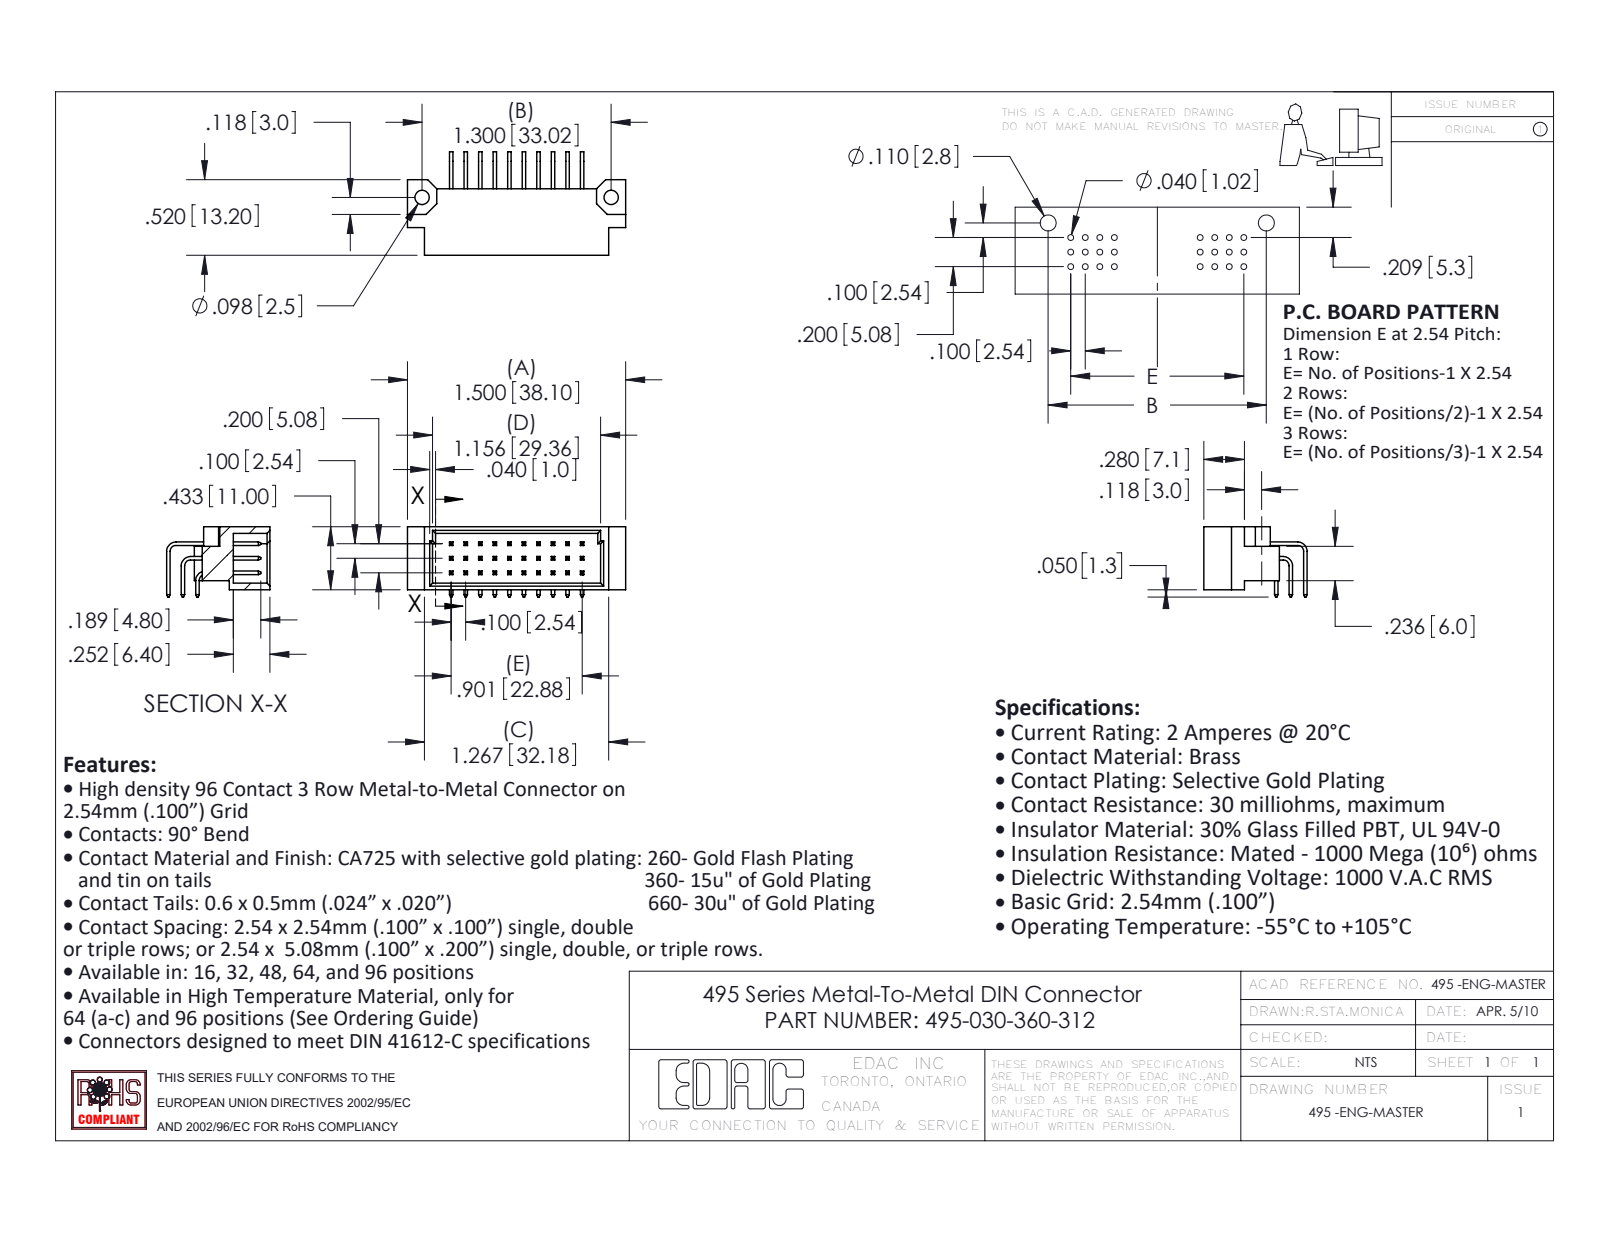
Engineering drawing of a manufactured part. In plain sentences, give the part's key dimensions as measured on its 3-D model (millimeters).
The part is named "495-030-360-312; 495-290-2; 495 Part_30; 495-290-3 (+1 more)". Its 3-D file was written by "SolidWorks 2020 (AUTOMOTIVE_DESIGN)". It is 31 solids with 709 faces: 645 planar, 64 cylindrical and 0 other. Overall it measures 38.1 by 18.05 by 12.27 millimeters. Its volume is 2 676 cubic millimeters and its surface area 4 287 square millimeters. Round holes: 2 of diameter 2.49. Partial cylindrical surfaces (rounded edges, fillets, slot ends): 3 of radius 1.02, 3 of radius 1.65. The main face-to-face distances are 2.54, 5.08, 7.62, 9.86, 0.61, 10.16, 5.2, 1.14, 12.7, 0.6. The hole center spacings are 33.02.
